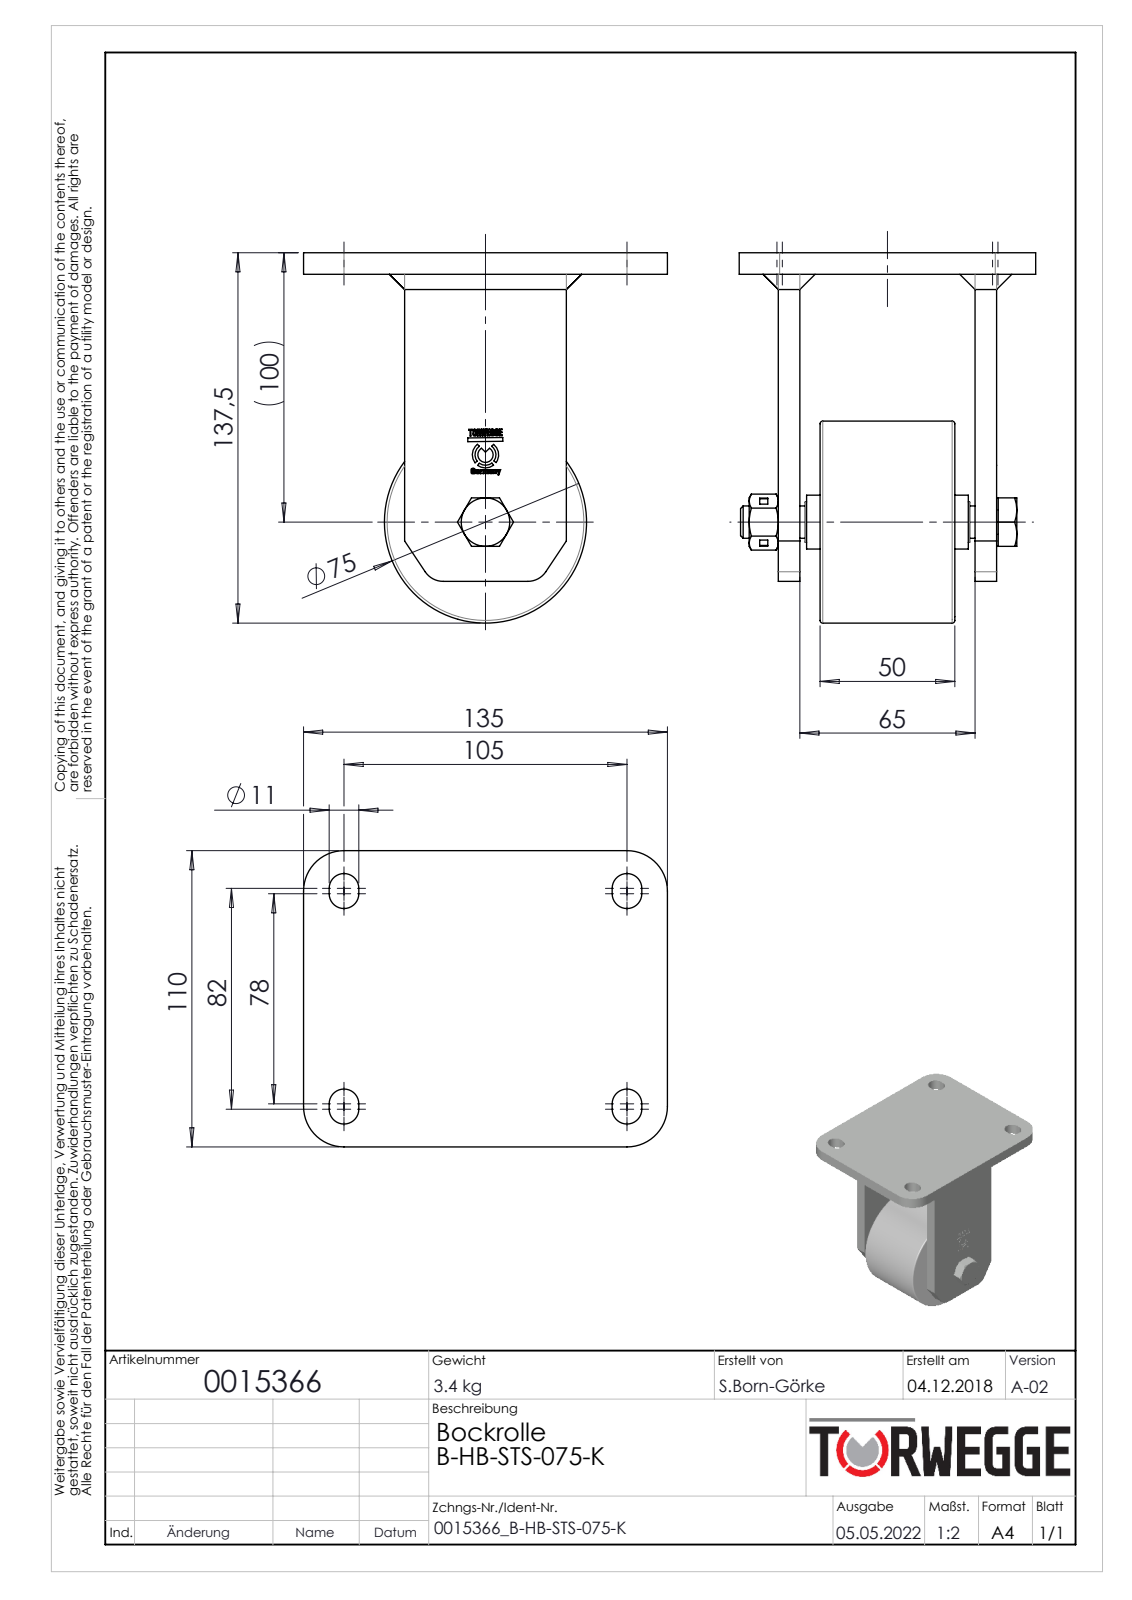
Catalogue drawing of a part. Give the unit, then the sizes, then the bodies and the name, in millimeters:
Units: millimetres
Overall size (bounding box): 137.5 × 135 × 110
Round holes (diameter × count): ⌀5.7 ×1, ⌀10.2 ×1, ⌀12 ×1, ⌀12.2 ×1, ⌀15 ×1, ⌀15.5 ×1, ⌀19.5 ×1, ⌀26.46 ×1, ⌀27.5 ×1, ⌀28 ×1, ⌀32 ×1
Round bosses / shafts (diameter × count): ⌀75 ×1, ⌀20.54 ×1, ⌀20 ×1, ⌀18 ×1
Partial cylindrical surfaces — rounded edges, fillets, slot ends (radius × count): R5.5 ×8, R15 ×4, R8 ×2, R3.9 ×1, R4.9 ×1
Main face-to-face distances: 8, 73, 15.5, 7.5, 65.5, 57.5, 81, 65, 50, 41
Hole centre spacings: 25
Volume: 439 629 mm³ · Surface area: 120 137 mm²
Bodies: 21 solids, 795 faces (390 planar, 111 cylindrical, 294 other)
Part name (STEP PRODUCT): 0015366
STEP written by: SolidWorks 2020 (AUTOMOTIVE_DESIGN)
